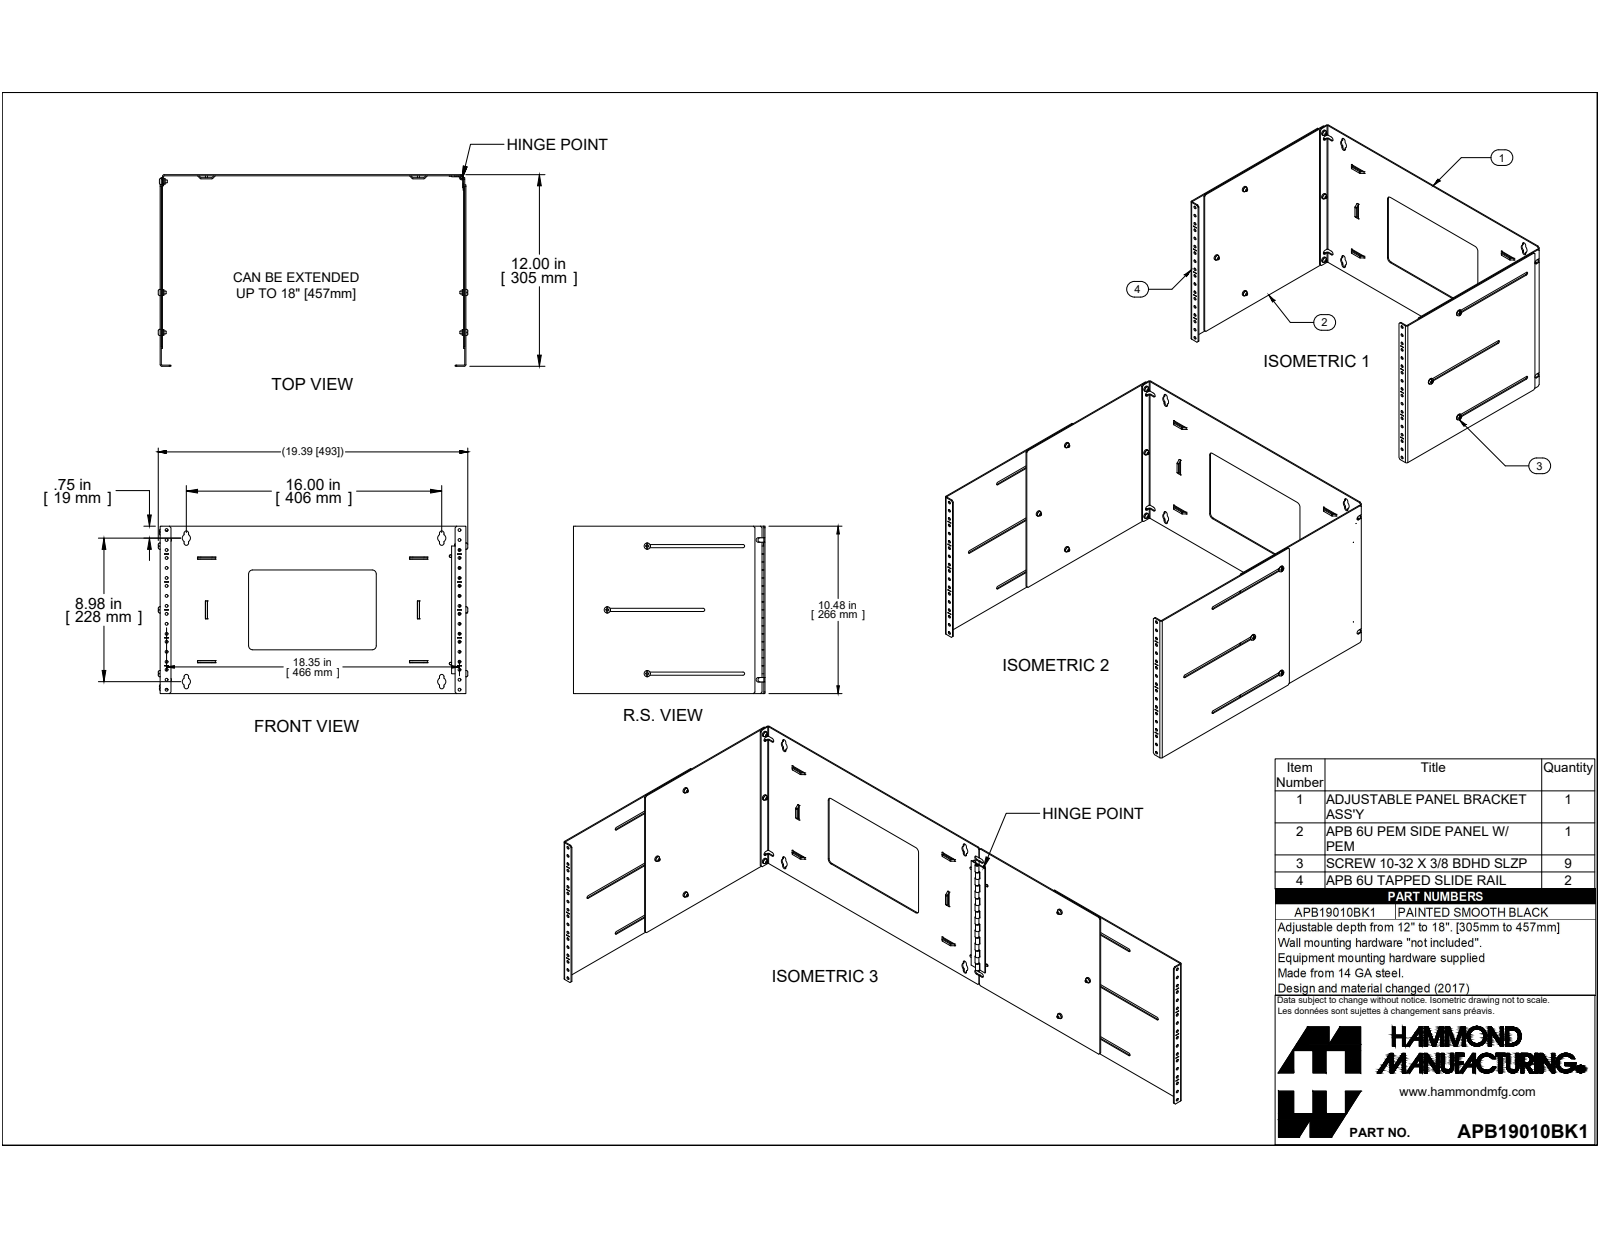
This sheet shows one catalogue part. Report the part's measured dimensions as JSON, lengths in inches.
{"part_name": "APB19010BK1", "step_written_by": "SolidWorks 2019 (CONFIG_CONTROL_DESIGN)", "units": "inches", "bodies": {"solids": 26, "faces": 732, "planar": 482, "cylindrical": 202, "other": 48}, "overall_size": [19.39, 12, 10.485], "volume_in3": 46.21, "surface_area_in2": 1322, "round_holes": [[0.177, 36], [0.159, 6], [0.25, 6], [0.201, 3], [0.133, 1]], "round_bosses_or_shafts": [[0.39, 6], [0.34, 6], [0.244, 6], [0.18, 6], [0.253, 1], [0.125, 1]], "partial_cylinders_radius": [[0.141, 16], [0.072, 12], [0.1, 6], [0.25, 4], [0.258, 4], [0.036, 3], [0.108, 3]], "face_to_face_distances": [0.072, 19.011, 19.083, 18.939, 18.867, 0.144, 0.072, 18.939, 19.155, 19.011], "hole_center_spacings": [1.75, 3.5, 18.361, 5.25, 18.35, 18.433, 18.681, 0.625]}
